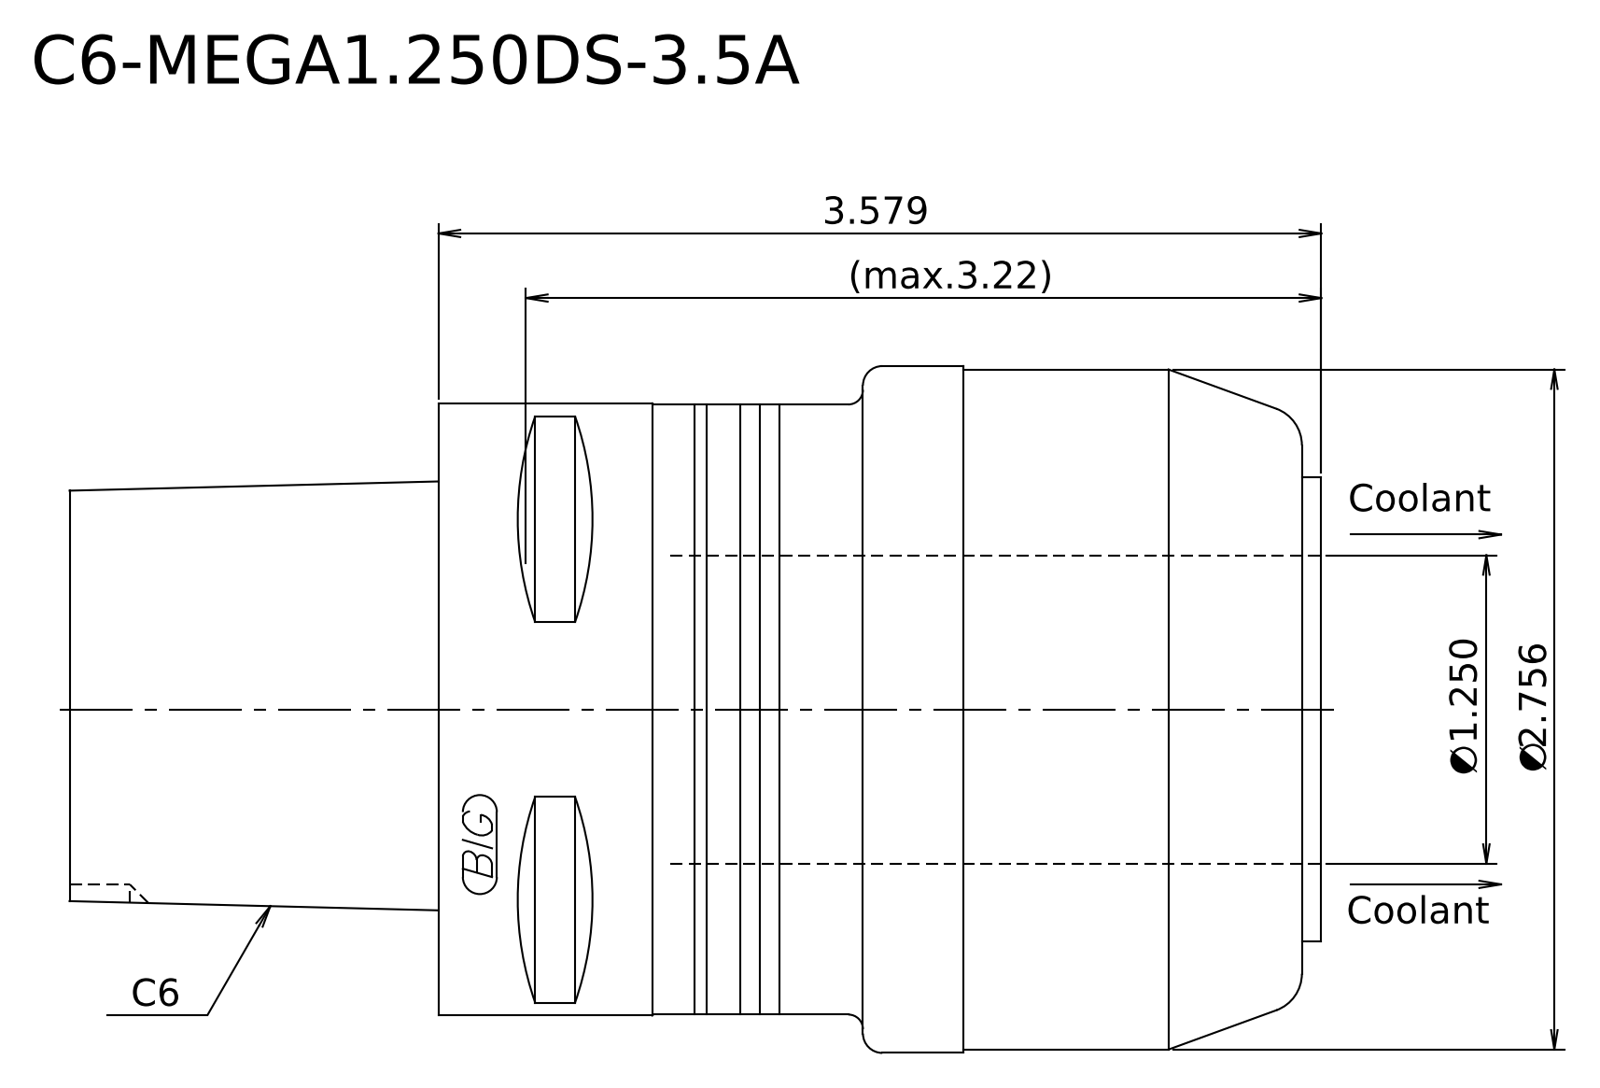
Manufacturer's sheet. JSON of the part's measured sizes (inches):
{"step_written_by": "Kubotek KeyCreator 2011 V10.0.2 (22737) (automotive_design)", "units": "inches", "bodies": {"solids": 1, "faces": 17, "planar": 6, "cylindrical": 5, "other": 6}, "overall_size": [5.075, 2.783, 2.783], "volume_in3": 22.09, "surface_area_in2": 47.4, "round_bosses_or_shafts": [[2.783, 1], [2.756, 1], [2.48, 1], [2.472, 1], [1.883, 1]], "face_to_face_distances": [3.579, 5.075, 1.496, 0.079, 3.5, 4.996, 1.858, 1.78, 1.72, 3.217]}
